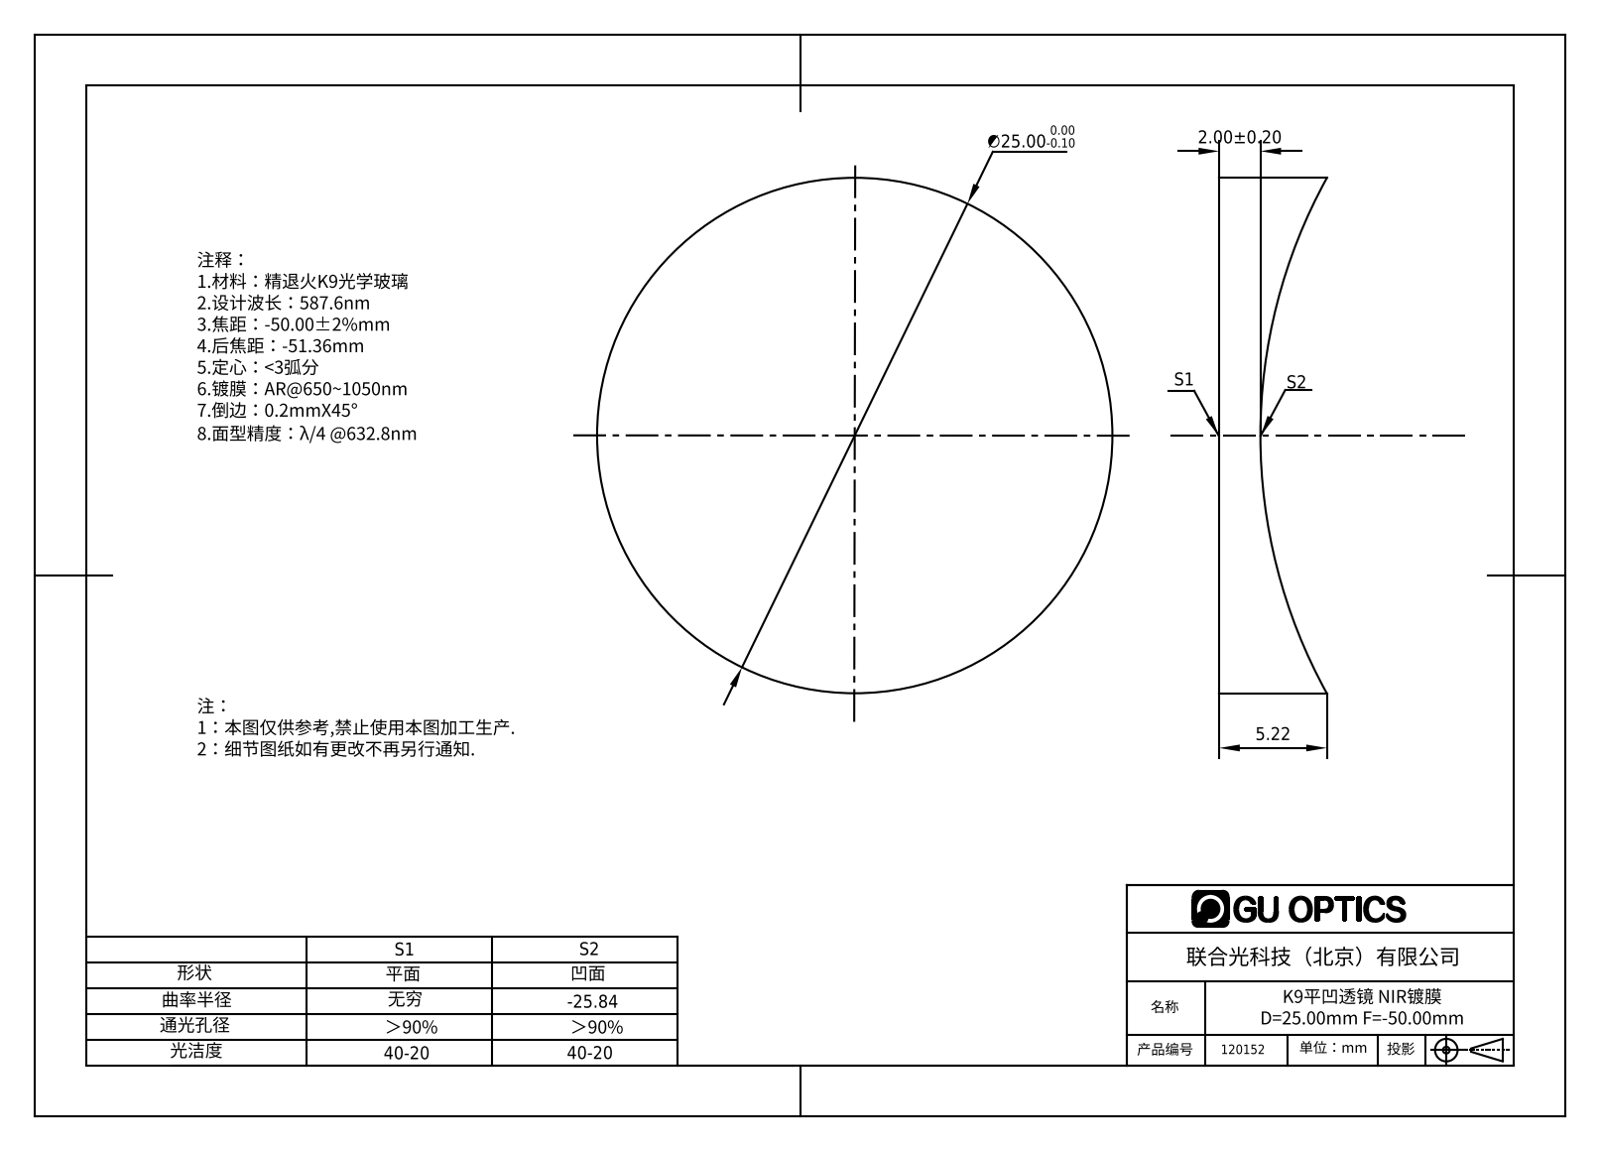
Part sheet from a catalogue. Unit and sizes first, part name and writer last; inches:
Units: inches
Overall size (bounding box): 0.984 × 0.984 × 0.206
Round bosses / shafts (diameter × count): ⌀0.984 ×1
Volume: 0.107 in³ · Surface area: 2.209 in²
Bodies: 1 solid, 5 faces (1 planar, 2 cylindrical, 2 other)
Part name (STEP PRODUCT): 120152
STEP written by: SolidWorks 2016 (AUTOMOTIVE_DESIGN)
